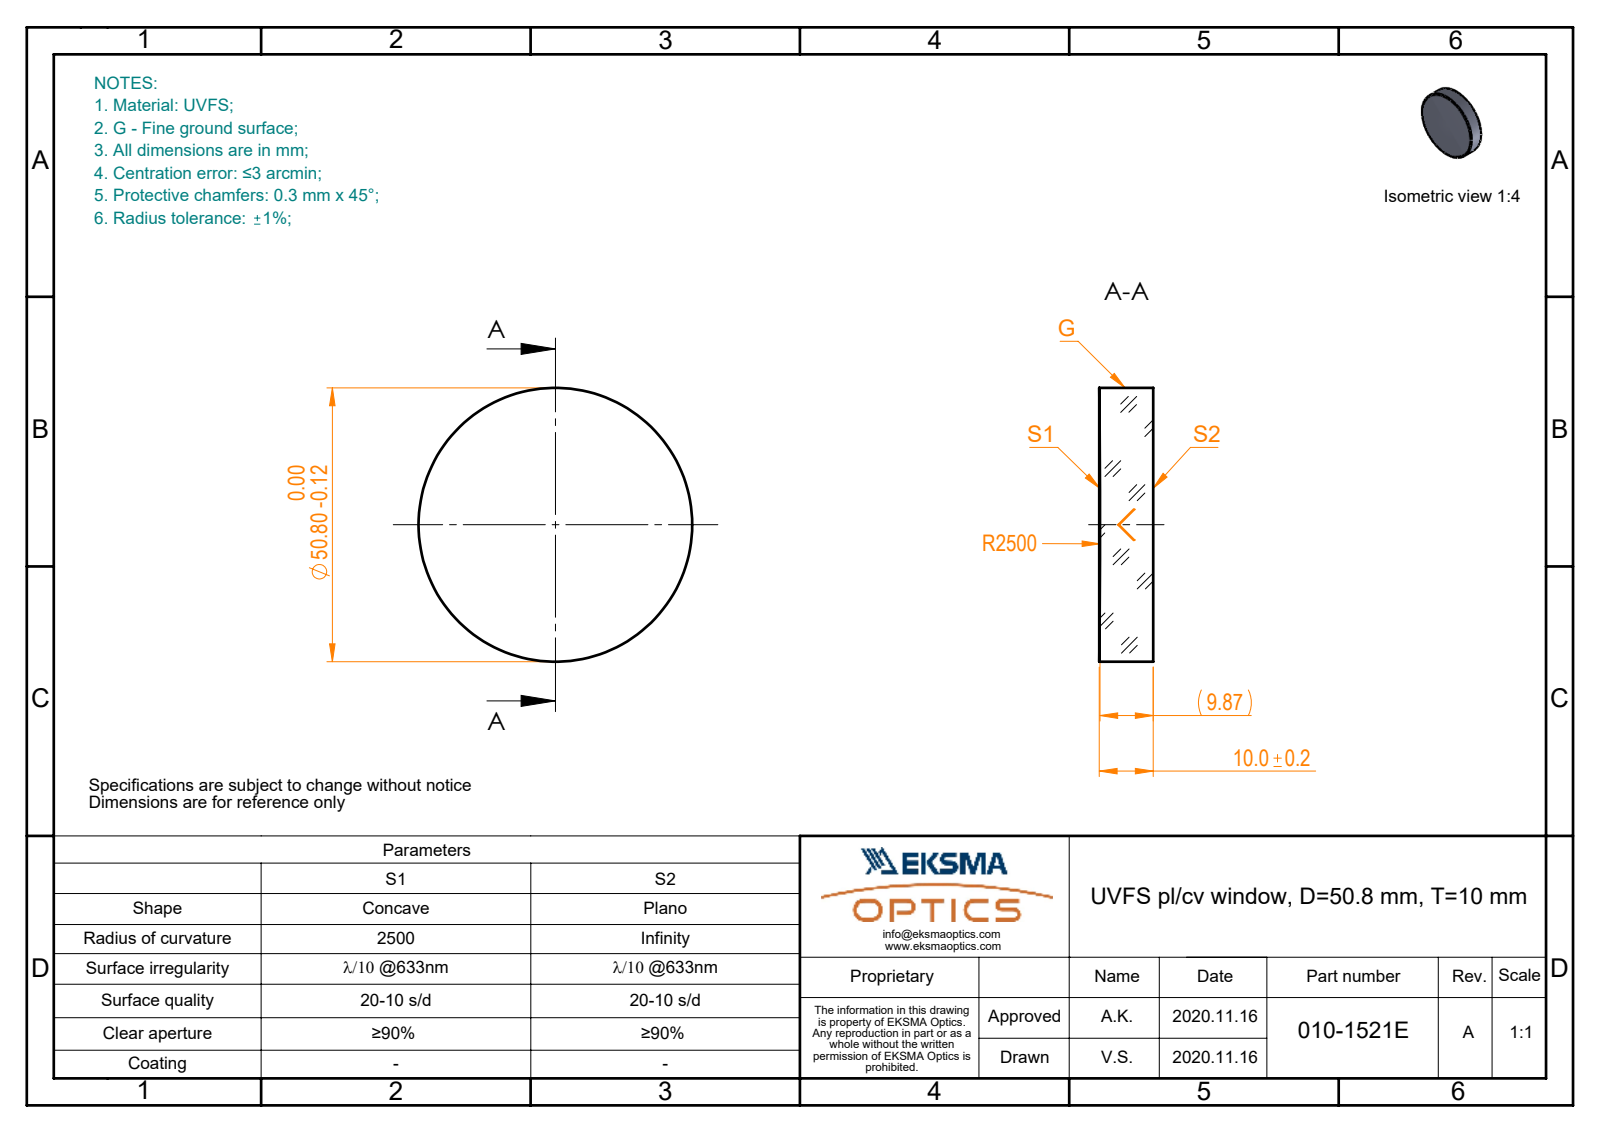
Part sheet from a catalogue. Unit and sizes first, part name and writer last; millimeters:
Units: millimetres
Overall size (bounding box): 50.8 × 50.8 × 10
Round bosses / shafts (diameter × count): ⌀50.8 ×1
Volume: 20 138 mm³ · Surface area: 5 650 mm²
Bodies: 1 solid, 5 faces (1 planar, 2 cylindrical, 2 other)
Part name (STEP PRODUCT): 010-1521E_UVFS_PCV_window
STEP written by: SolidWorks 2019 (CONFIG_CONTROL_DESIGN)
